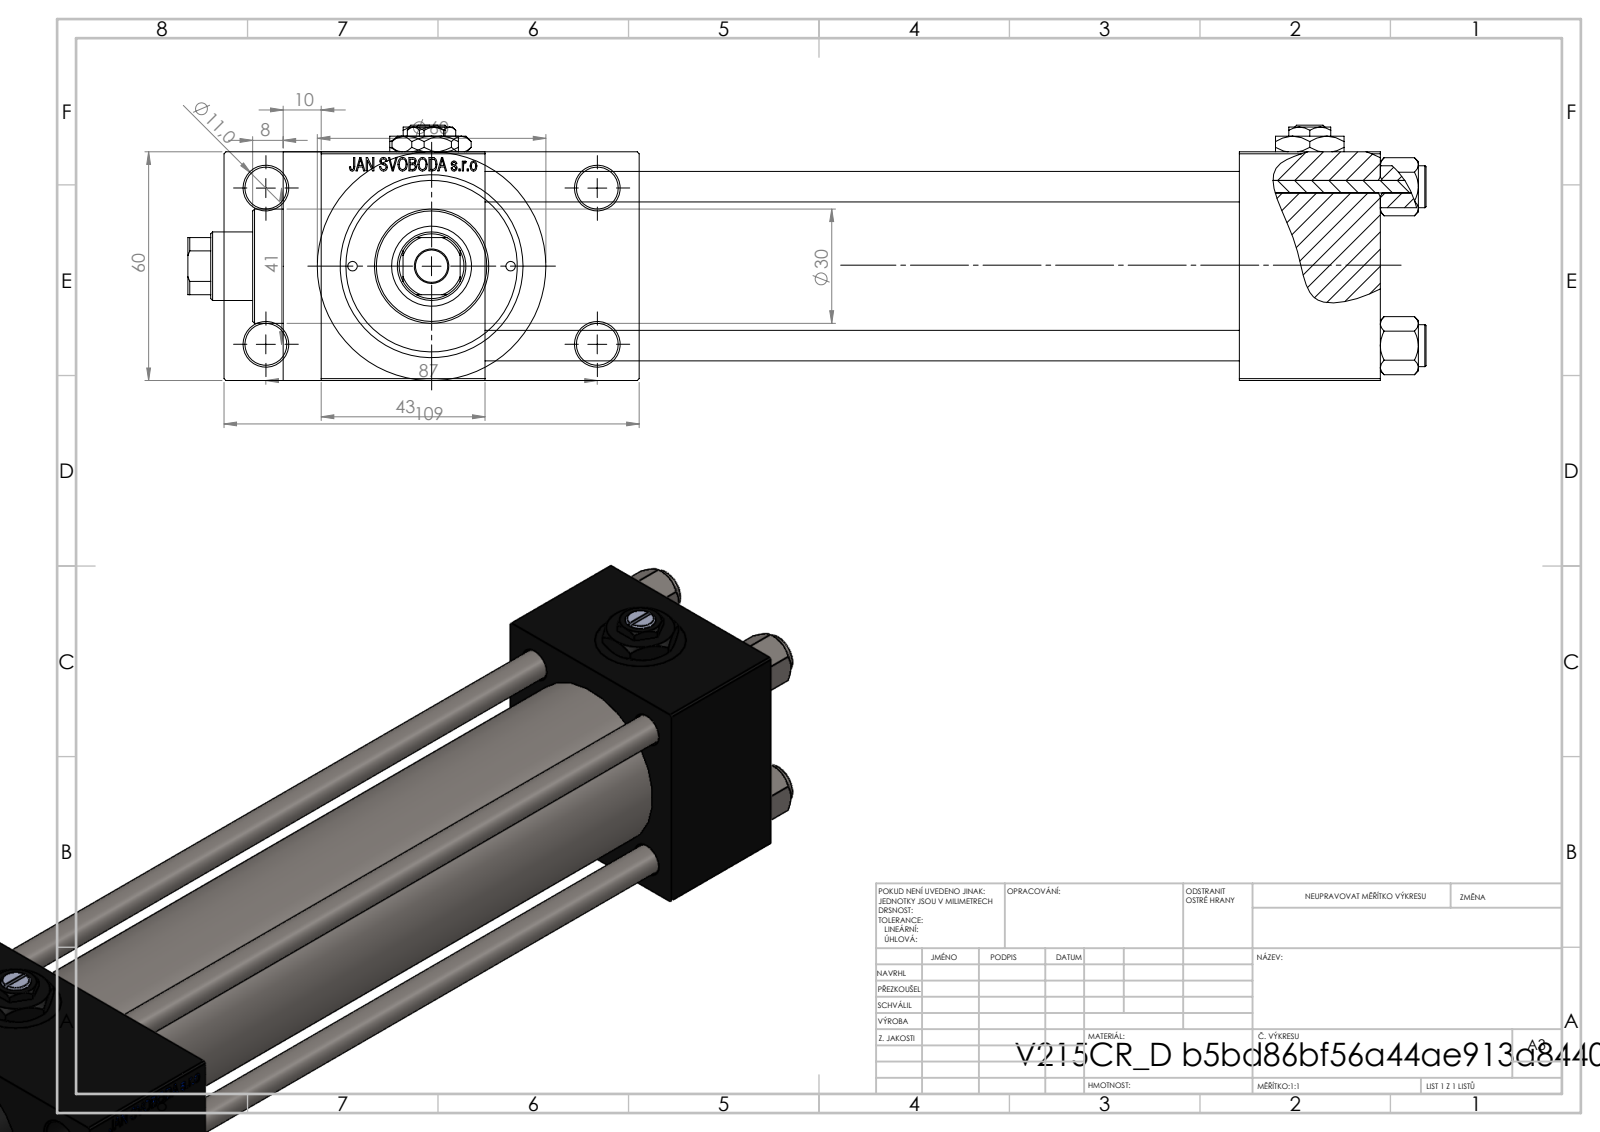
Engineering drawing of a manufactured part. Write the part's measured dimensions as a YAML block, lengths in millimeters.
part_name: "V215CR_D_Body; Zatka_pro_OIL_PORT; V215_VC_A; V215CR_D_TYCINKA (+2 more)"
step_written_by: "SolidWorks 2019 (CONFIG_CONTROL_DESIGN)"
units: millimeters
bodies: {solids: 13, faces: 1214, planar: 548, cylindrical: 104, other: 562}
overall_size: [325, 109, 67]
volume: 635892
surface_area: 183688
round_holes:
  - {diameter: 8, count: 4}
  - {diameter: 11, count: 4}
  - {diameter: 2.5, count: 2}
  - {diameter: 7, count: 2}
  - {diameter: 16.66, count: 2}
  - {diameter: 24, count: 2}
  - {diameter: 8.5, count: 1}
  - {diameter: 18, count: 1}
  - {diameter: 21, count: 1}
  - {diameter: 31, count: 1}
  - {diameter: 40, count: 1}
  - {diameter: 45, count: 1}
round_bosses_or_shafts:
  - {diameter: 11, count: 4}
  - {diameter: 60, count: 1}
  - {diameter: 46, count: 1}
  - {diameter: 30, count: 1}
partial_cylinders:
  - {radius: 8.5, count: 1}
face_to_face_distances: [60, 24.5, 84.5, 198, 37, 235, 43, 278, 241, 109]
hole_center_spacings: [20.85, 22.65, 29.49, 30.62, 41.7, 46.53, 47.15, 48.09]
